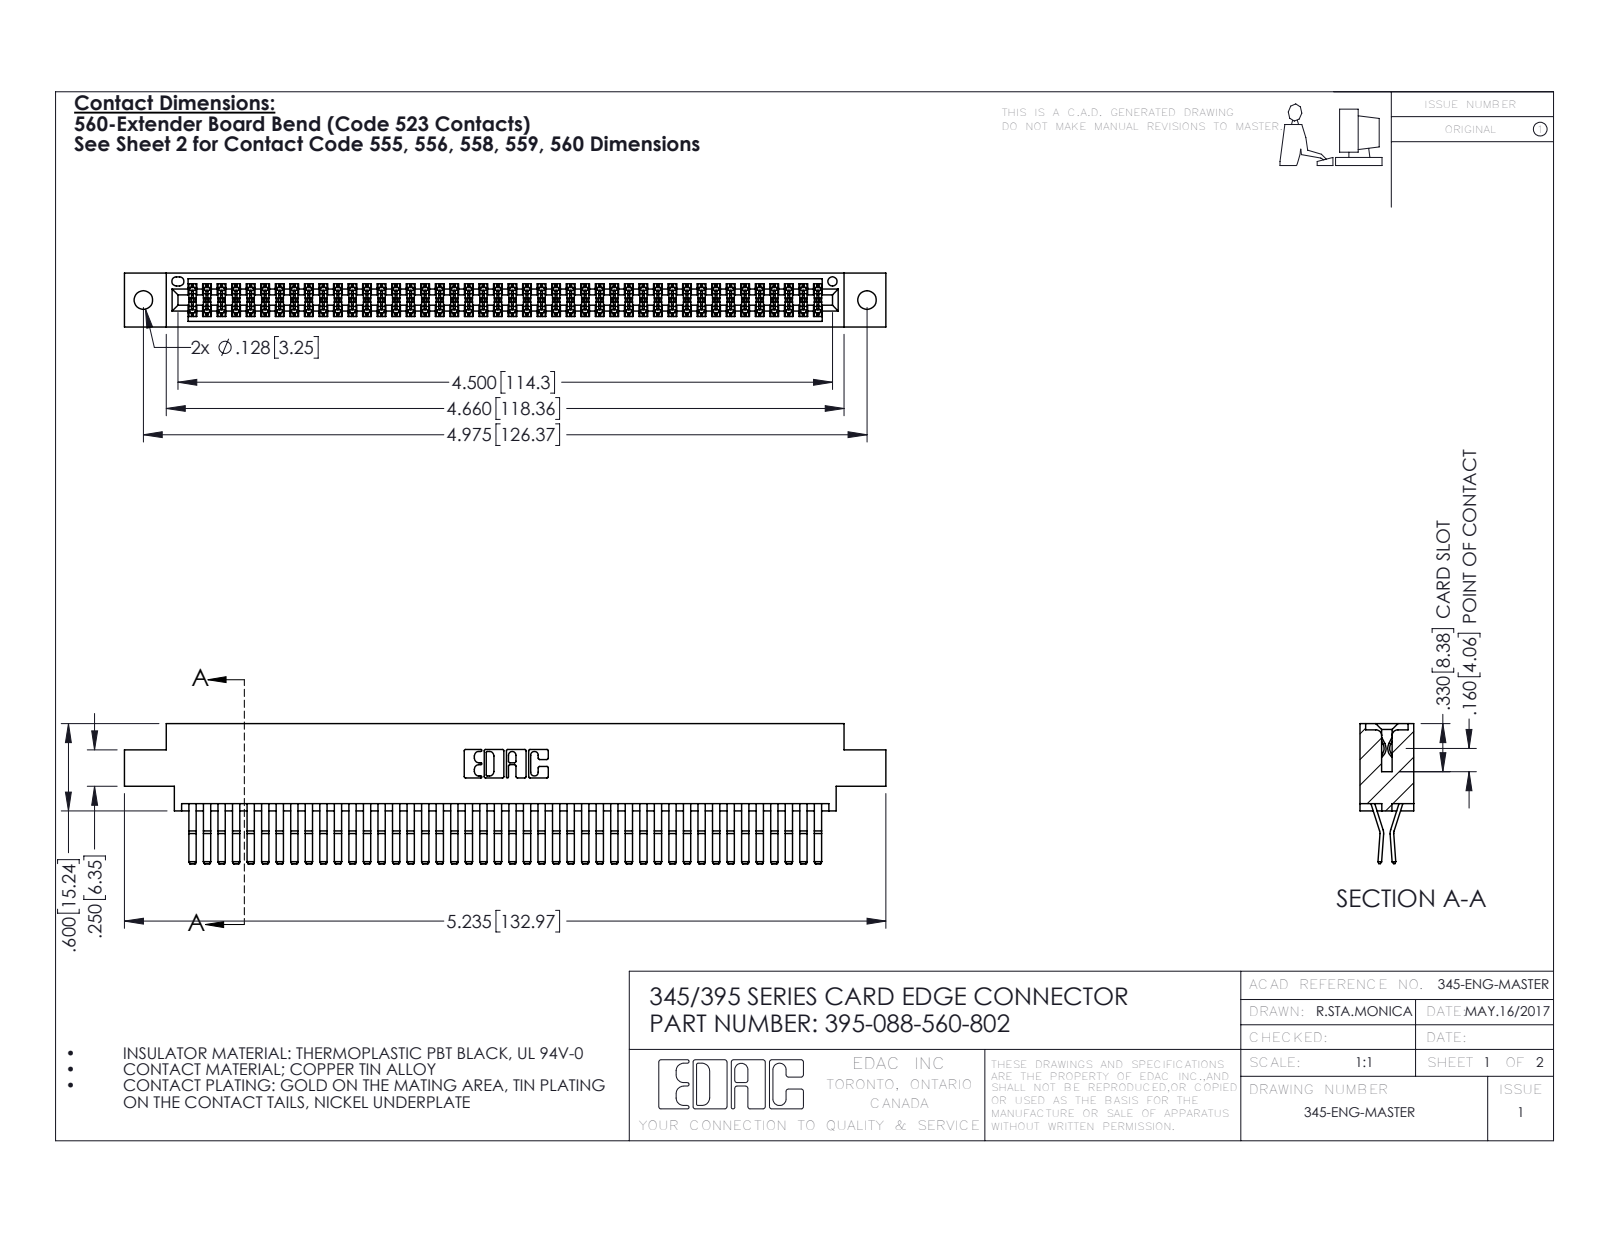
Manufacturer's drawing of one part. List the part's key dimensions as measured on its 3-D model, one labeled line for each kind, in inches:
Part name (STEP PRODUCT): 395-088-560-802; 345-292-001_560 Tail; 345 Part_0.170 Offset - 0.128 Dia
STEP written by: SolidWorks 2016 (CONFIG_CONTROL_DESIGN)
Units: inches
Bodies: 89 solids, 4706 faces (2988 planar, 1718 cylindrical, 0 other)
Overall size (bounding box): 5.235 × 0.962 × 0.37
Volume: 0.815 in³ · Surface area: 32.77 in²
Round holes (diameter × count): ⌀0.128 ×2, ⌀0.064 ×1
Partial cylindrical surfaces — rounded edges, fillets, slot ends (radius × count): R0.006 ×132, R0.01 ×22, R0.007 ×6, R0.031 ×6, R0.026 ×3, R0.01 ×2, R0.014 ×2, R0.019 ×2
Main face-to-face distances: 0.025, 0.298, 0.072, 0.37, 0.2, 0.098, 0.272, 0.225, 0.175, 0.149
Hole centre spacings: 0.27, 4.739, 4.975
